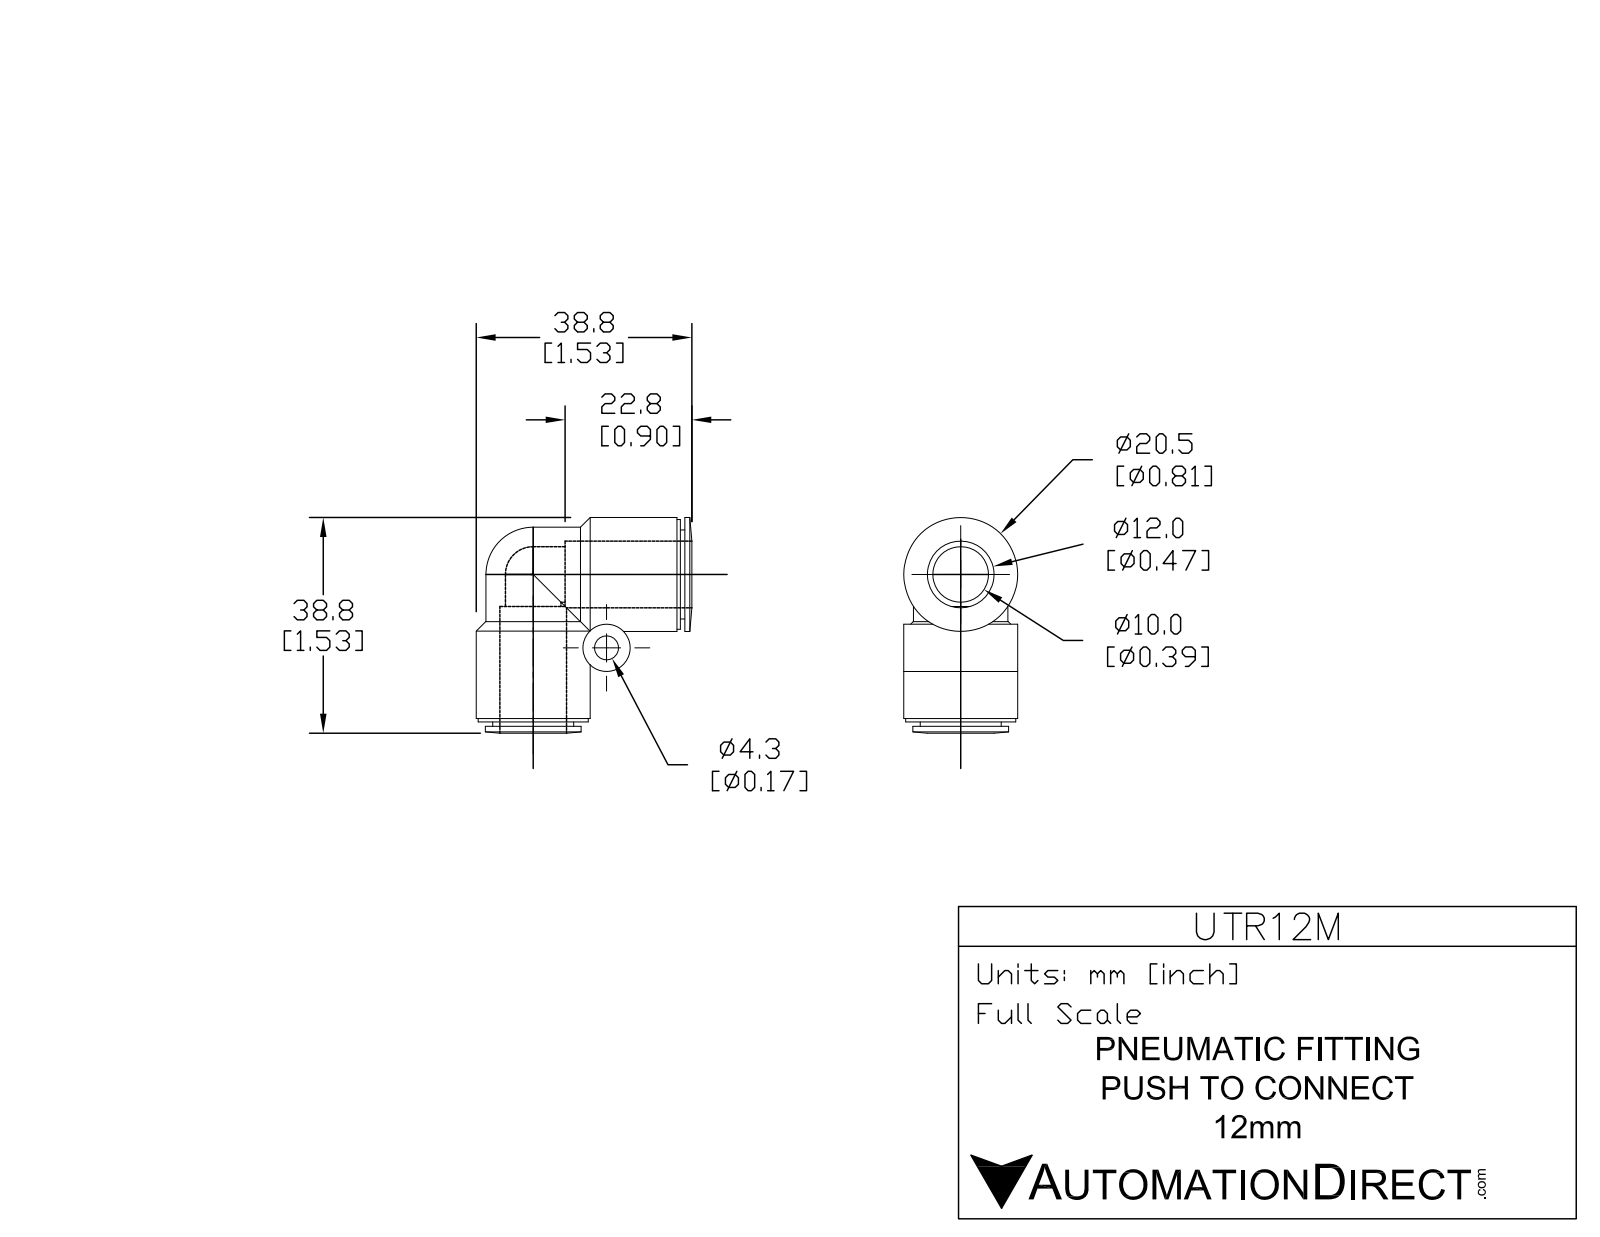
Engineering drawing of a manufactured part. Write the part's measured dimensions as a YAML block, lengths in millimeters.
part_name: "UL16M"
step_written_by: "SolidWorks 2015 (CONFIG_CONTROL_DESIGN)"
units: millimeters
bodies: {solids: 1, faces: 57, planar: 9, cylindrical: 33, other: 15}
overall_size: [47.05, 47.05, 25.5]
volume: 17593
surface_area: 10373
round_holes:
  - {diameter: 13, count: 2}
  - {diameter: 16, count: 2}
  - {diameter: 5.3, count: 1}
round_bosses_or_shafts:
  - {diameter: 25.5, count: 2}
  - {diameter: 20, count: 2}
  - {diameter: 24.54, count: 1}
  - {diameter: 24.46, count: 1}
  - {diameter: 18, count: 1}
  - {diameter: 8.5, count: 1}
face_to_face_distances: [1, 21.83, 22.83, 22.6, 21.6, 25.5, 22.75, 21.75]
